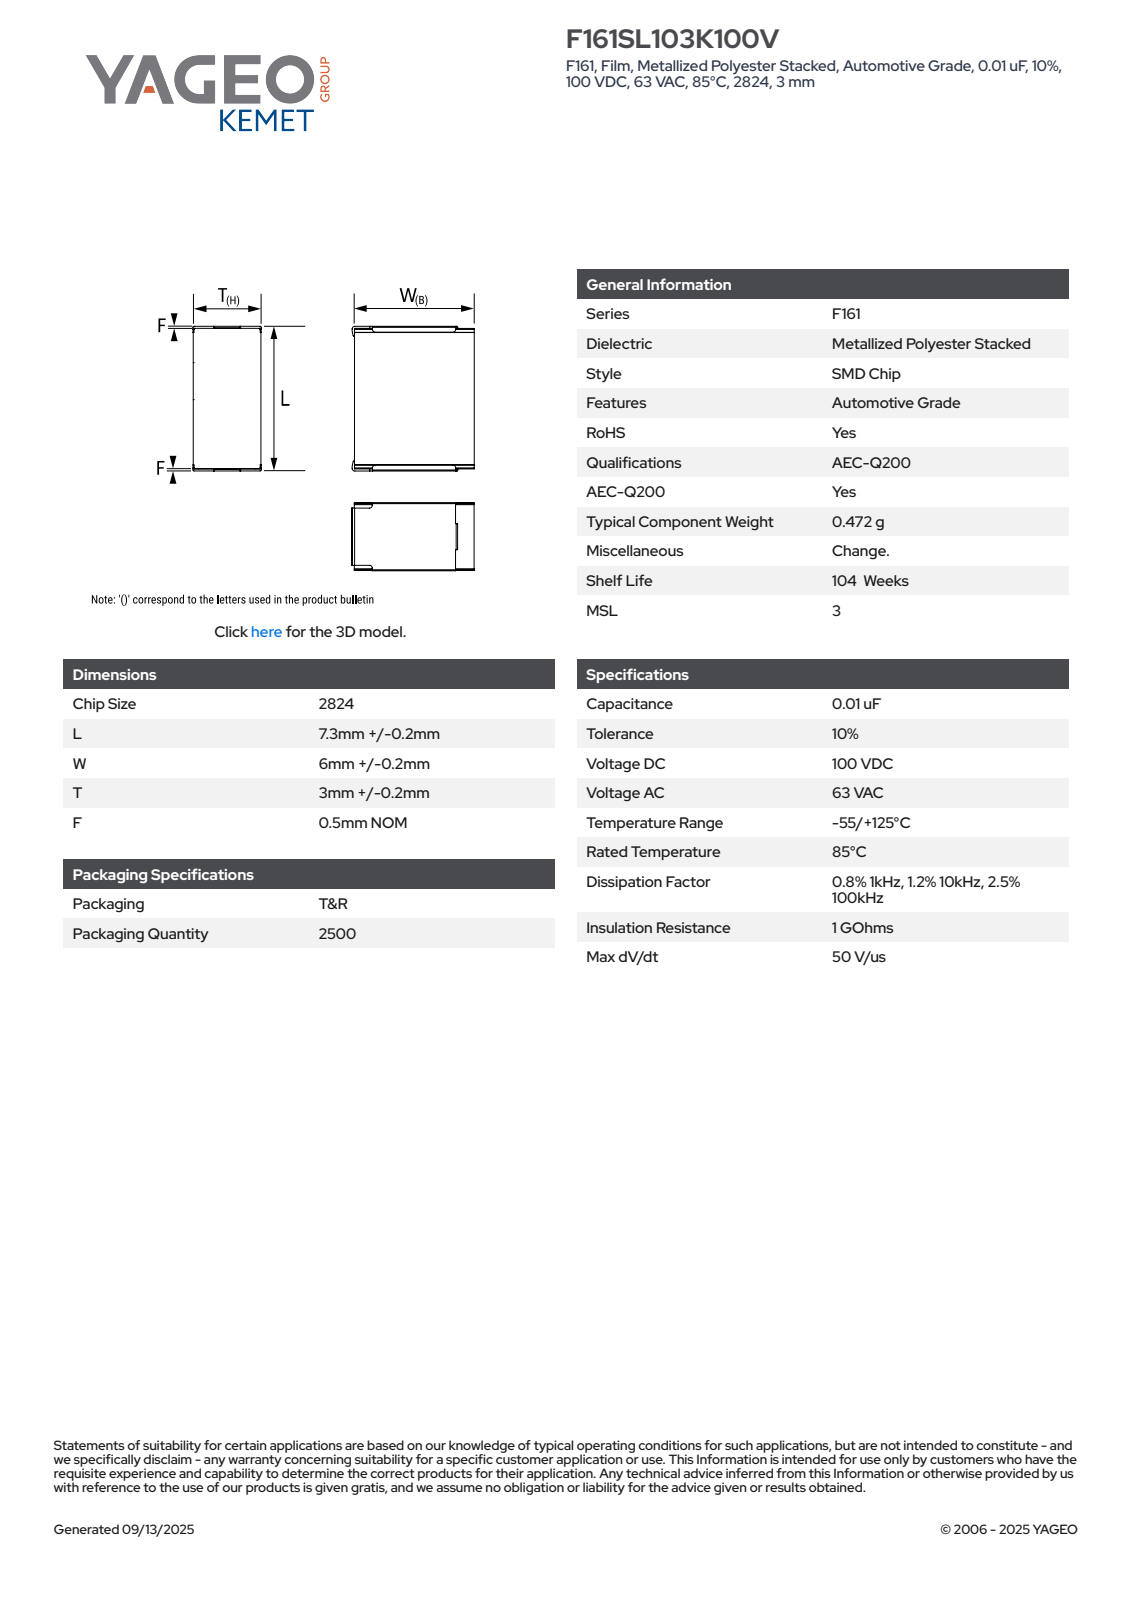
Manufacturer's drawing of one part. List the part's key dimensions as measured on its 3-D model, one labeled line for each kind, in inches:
Part name (STEP PRODUCT): CFS_KSTD_2824_L7.5W6.2T3.2F0.5
STEP written by: SolidWorks 2021 (AUTOMOTIVE_DESIGN)
Units: inches
Bodies: 4 solids, 117 faces (103 planar, 14 cylindrical, 0 other)
Overall size (bounding box): 0.295 × 0.252 × 0.132
Volume: 0.009 in³ · Surface area: 0.293 in²
Partial cylindrical surfaces — rounded edges, fillets, slot ends (radius × count): R0.007 ×10, R0.01 ×4
Main face-to-face distances: 0.126, 0.234, 0.295, 0.02, 0.276, 0.129, 0.018, 0.256, 0.132, 0.252
